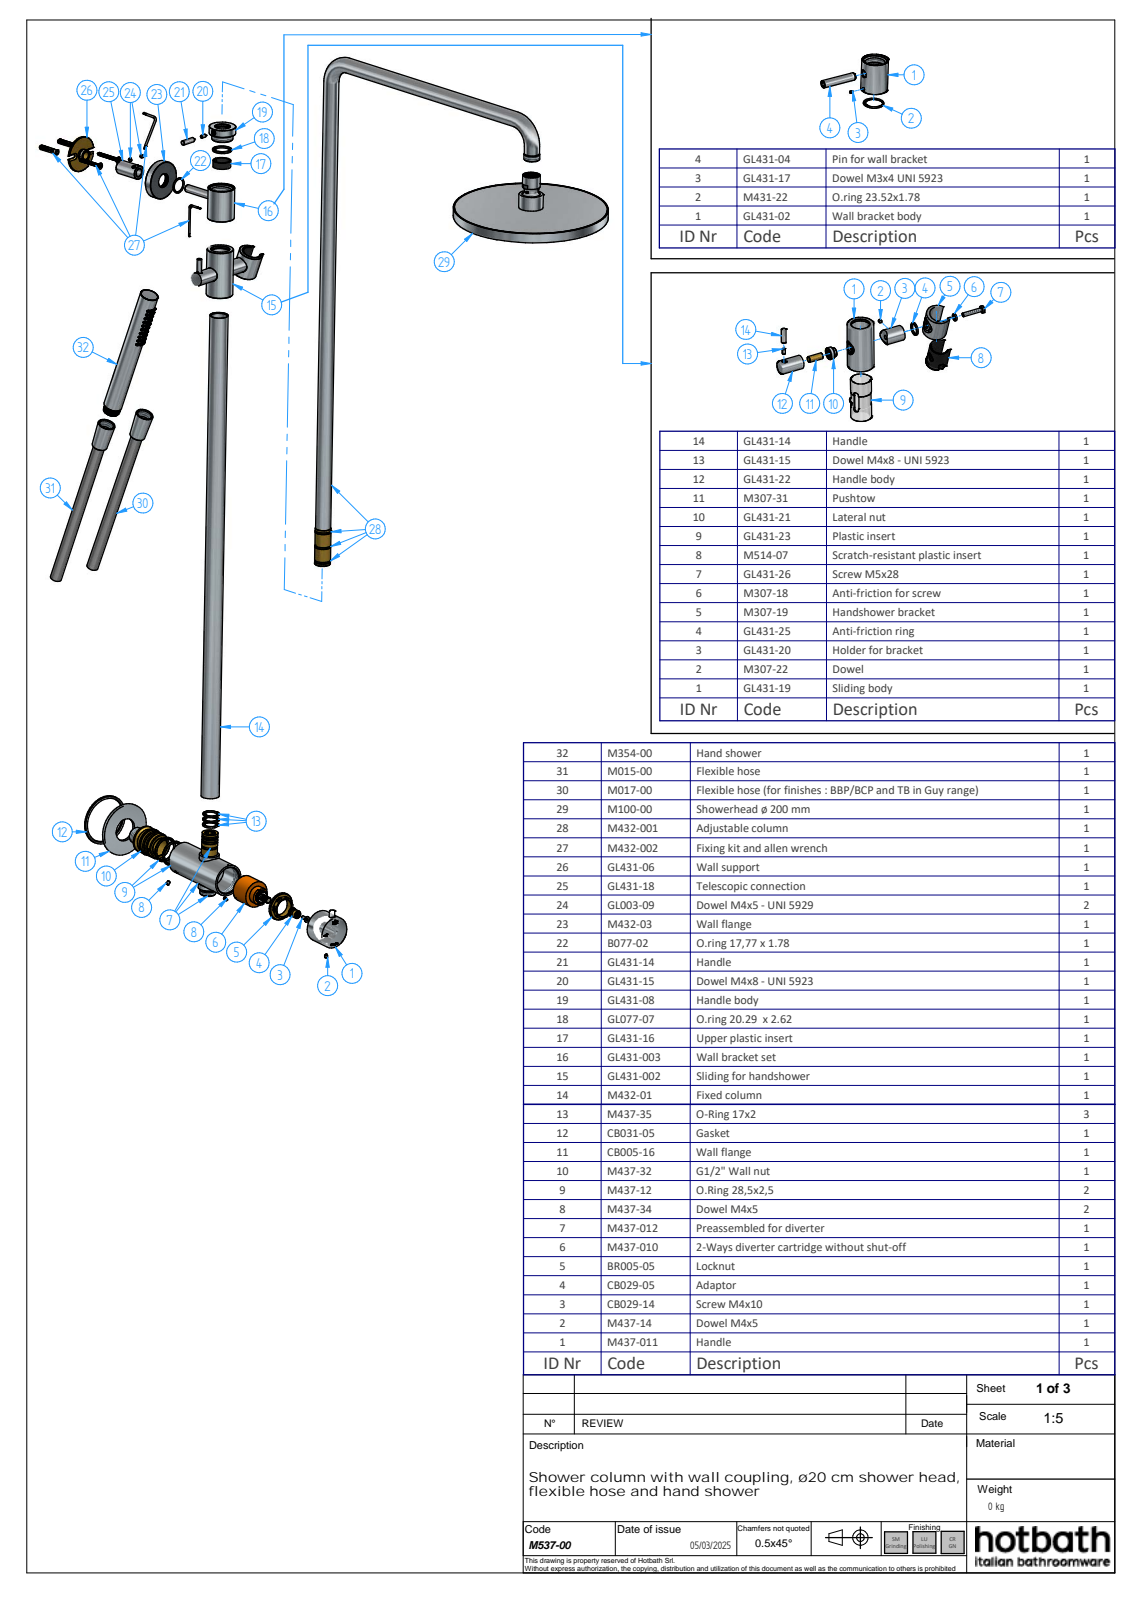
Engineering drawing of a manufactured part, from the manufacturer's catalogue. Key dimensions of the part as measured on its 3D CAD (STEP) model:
Part name (STEP PRODUCT): M537-00; M438-001_oa_0; CB005-16; M437-34 (+8 more)
STEP written by: Solid Edge (AUTOMOTIVE_DESIGN)
Units: millimetres
Bodies: 35 solids, 1929 faces (582 planar, 604 cylindrical, 743 other)
Overall size (bounding box): 1465.69 × 547.98 × 203.5
Volume: 545 274 mm³ · Surface area: 535 084 mm²
Round holes (diameter × count): ⌀4.5 ×126, ⌀3.2 ×40, ⌀3.3 ×7, ⌀3.24 ×5, ⌀5 ×5, ⌀16.5 ×4, ⌀18.5 ×4, ⌀17 ×3, ⌀6.5 ×2, ⌀7 ×2, ⌀8 ×2, ⌀10.5 ×2
Round bosses / shafts (diameter × count): ⌀7 ×5, ⌀4 ×5, ⌀20 ×3, ⌀18 ×3, ⌀6 ×3, ⌀15 ×2, ⌀203.5 ×1, ⌀70 ×1
Partial cylindrical surfaces — rounded edges, fillets, slot ends (radius × count): R0.2 ×51, R0.5 ×6, R0.35 ×4, R0.59 ×3, R0.77 ×3, R0.22 ×2, R0.23 ×2, R0.28 ×2
Main face-to-face distances: 1, 0.5, 3.2, 1.41, 2.7, 1.91, 1.29, 0.9, 2.3, 1.8
Hole centre spacings: 12, 7.21, 4, 6, 12.65, 10, 9, 14.42
